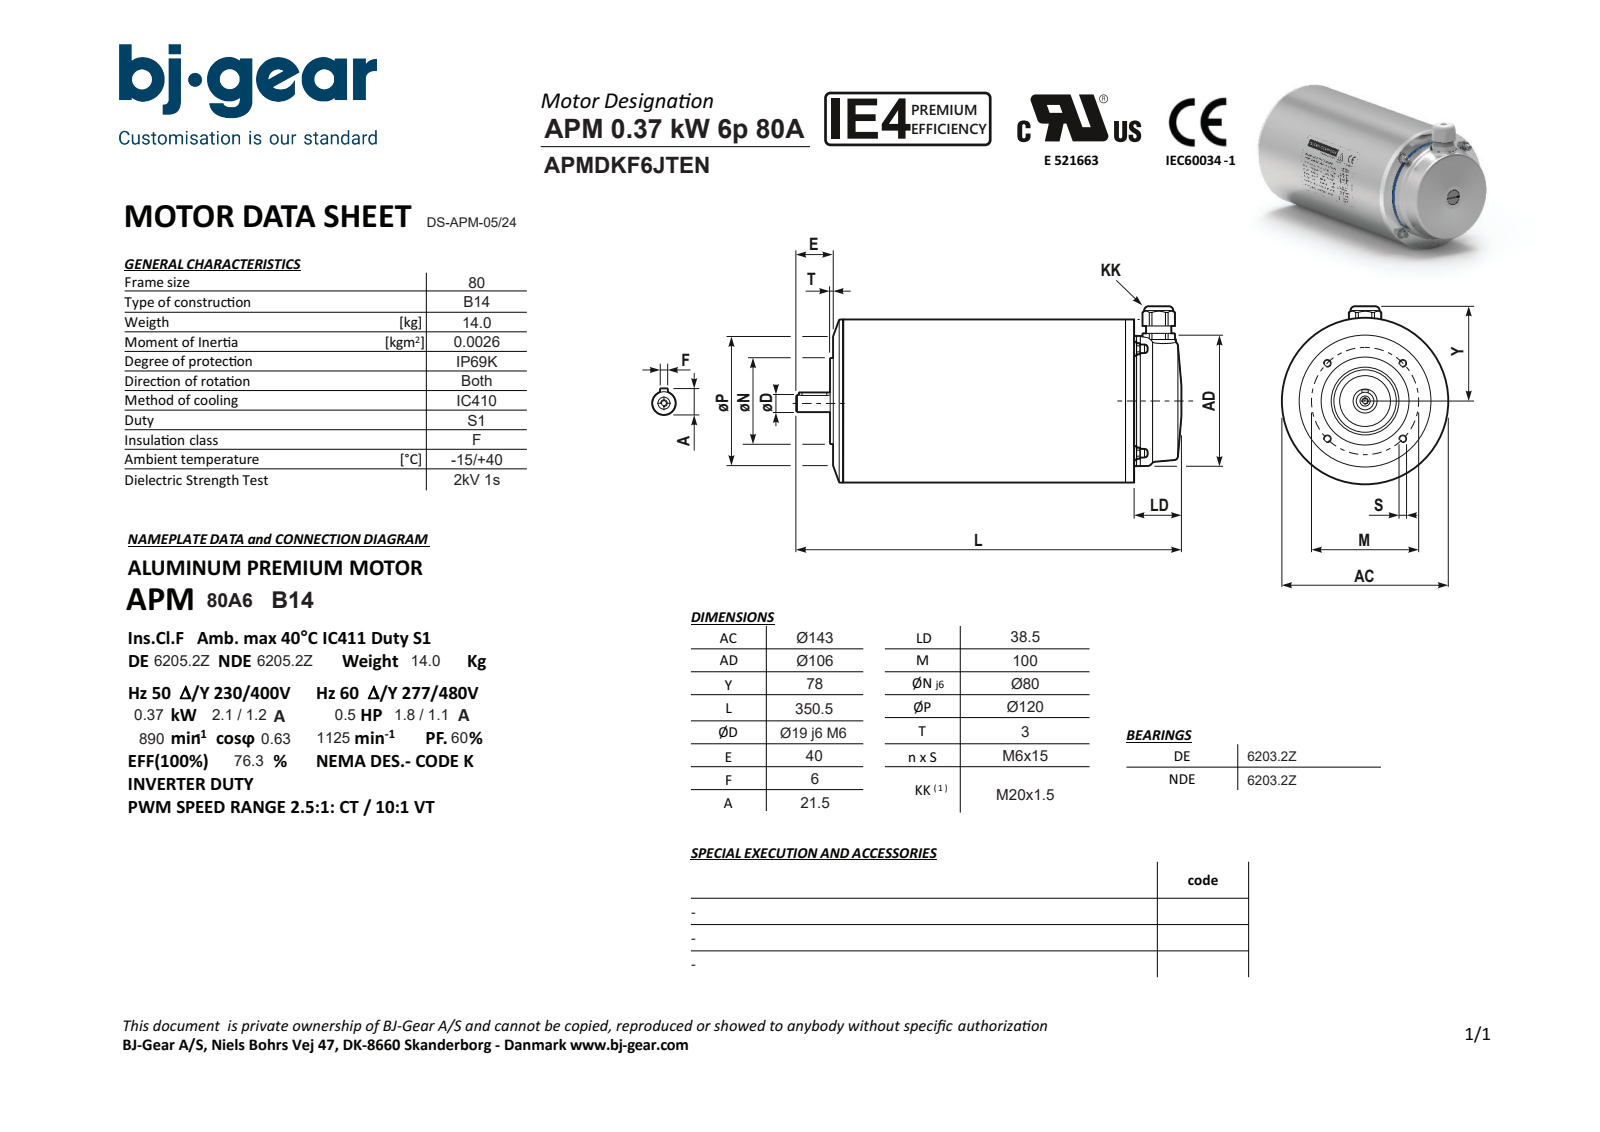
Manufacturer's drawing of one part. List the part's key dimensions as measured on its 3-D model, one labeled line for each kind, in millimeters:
Part name (STEP PRODUCT): APMDKF6JTENN4KCR2-N---NNN
STEP written by: Solid Edge (AUTOMOTIVE_DESIGN)
Units: millimetres
Bodies: 1 solid, 156 faces (75 planar, 50 cylindrical, 31 other)
Overall size (bounding box): 350.5 × 148.3 × 142.6
Volume: 4 636 000 mm³ · Surface area: 172 344 mm²
Round holes (diameter × count): ⌀4.92 ×5, ⌀6.4 ×1, ⌀16 ×1, ⌀28 ×1, ⌀65 ×1
Round bosses / shafts (diameter × count): ⌀11.5 ×4, ⌀7 ×4, ⌀142.6 ×1, ⌀142.6 ×1, ⌀106 ×1, ⌀80 ×1, ⌀25 ×1, ⌀23.7 ×1
Partial cylindrical surfaces — rounded edges, fillets, slot ends (radius × count): R3 ×2, R13.2 ×1
Main face-to-face distances: 272, 6, 266, 9, 3, 275, 24, 310.5, 38.5, 304.5
Hole centre spacings: 50.01, 70.72, 100.01
